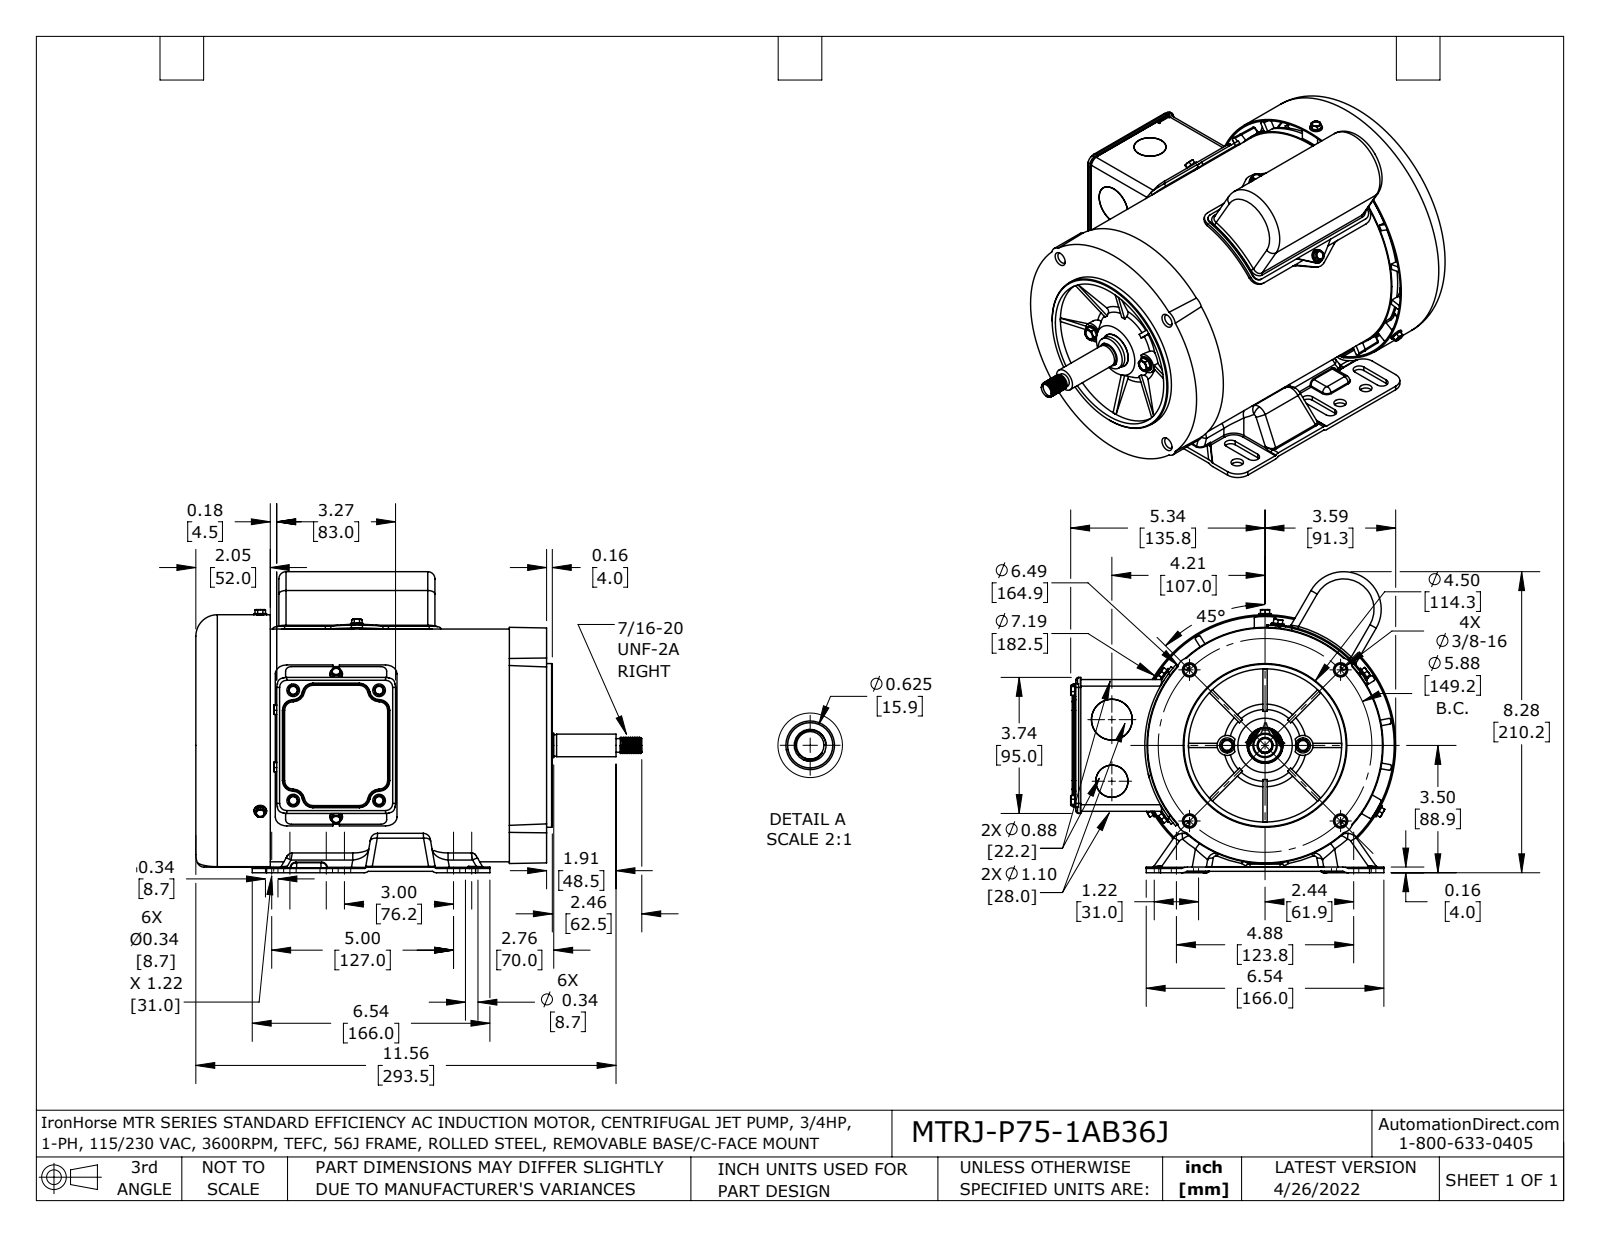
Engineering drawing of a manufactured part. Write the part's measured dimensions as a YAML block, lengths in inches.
part_name: "MTRJ-P75-1AB36J redcmb1 coord"
step_written_by: "SolidWorks 2021 (AUTOMOTIVE_DESIGN)"
units: inches
bodies: {solids: 34, faces: 2940, planar: 731, cylindrical: 966, other: 1243}
overall_size: [12.264, 8.938, 8.276]
volume: 47.59
surface_area: 982.9
round_holes:
  - {diameter: 0.219, count: 13}
  - {diameter: 0.197, count: 12}
  - {diameter: 0.276, count: 8}
  - {diameter: 0.177, count: 6}
  - {diameter: 0.217, count: 6}
  - {diameter: 0.328, count: 6}
  - {diameter: 0.344, count: 6}
  - {diameter: 0.136, count: 5}
  - {diameter: 0.15, count: 4}
  - {diameter: 0.313, count: 4}
  - {diameter: 0.709, count: 3}
  - {diameter: 0.13, count: 2}
round_bosses_or_shafts:
  - {diameter: 0.164, count: 13}
  - {diameter: 0.348, count: 10}
  - {diameter: 0.236, count: 6}
  - {diameter: 0.348, count: 3}
  - {diameter: 0.414, count: 2}
  - {diameter: 0.19, count: 2}
  - {diameter: 7.185, count: 1}
  - {diameter: 6.398, count: 1}
partial_cylinders:
  - {radius: 0.118, count: 113}
  - {radius: 0.039, count: 57}
  - {radius: 0.157, count: 32}
  - {radius: 0.02, count: 30}
  - {radius: 0.138, count: 26}
  - {radius: 0.197, count: 20}
  - {radius: 0.079, count: 18}
  - {radius: 0.276, count: 18}
face_to_face_distances: [0.039, 0.118, 0.063, 0.031, 9.646, 9.606, 0.157, 3.559, 0.079, 3.087]
hole_center_spacings: [4.221, 3.031, 0.094, 2.32, 2.409, 2.937, 3.748, 3.841]
